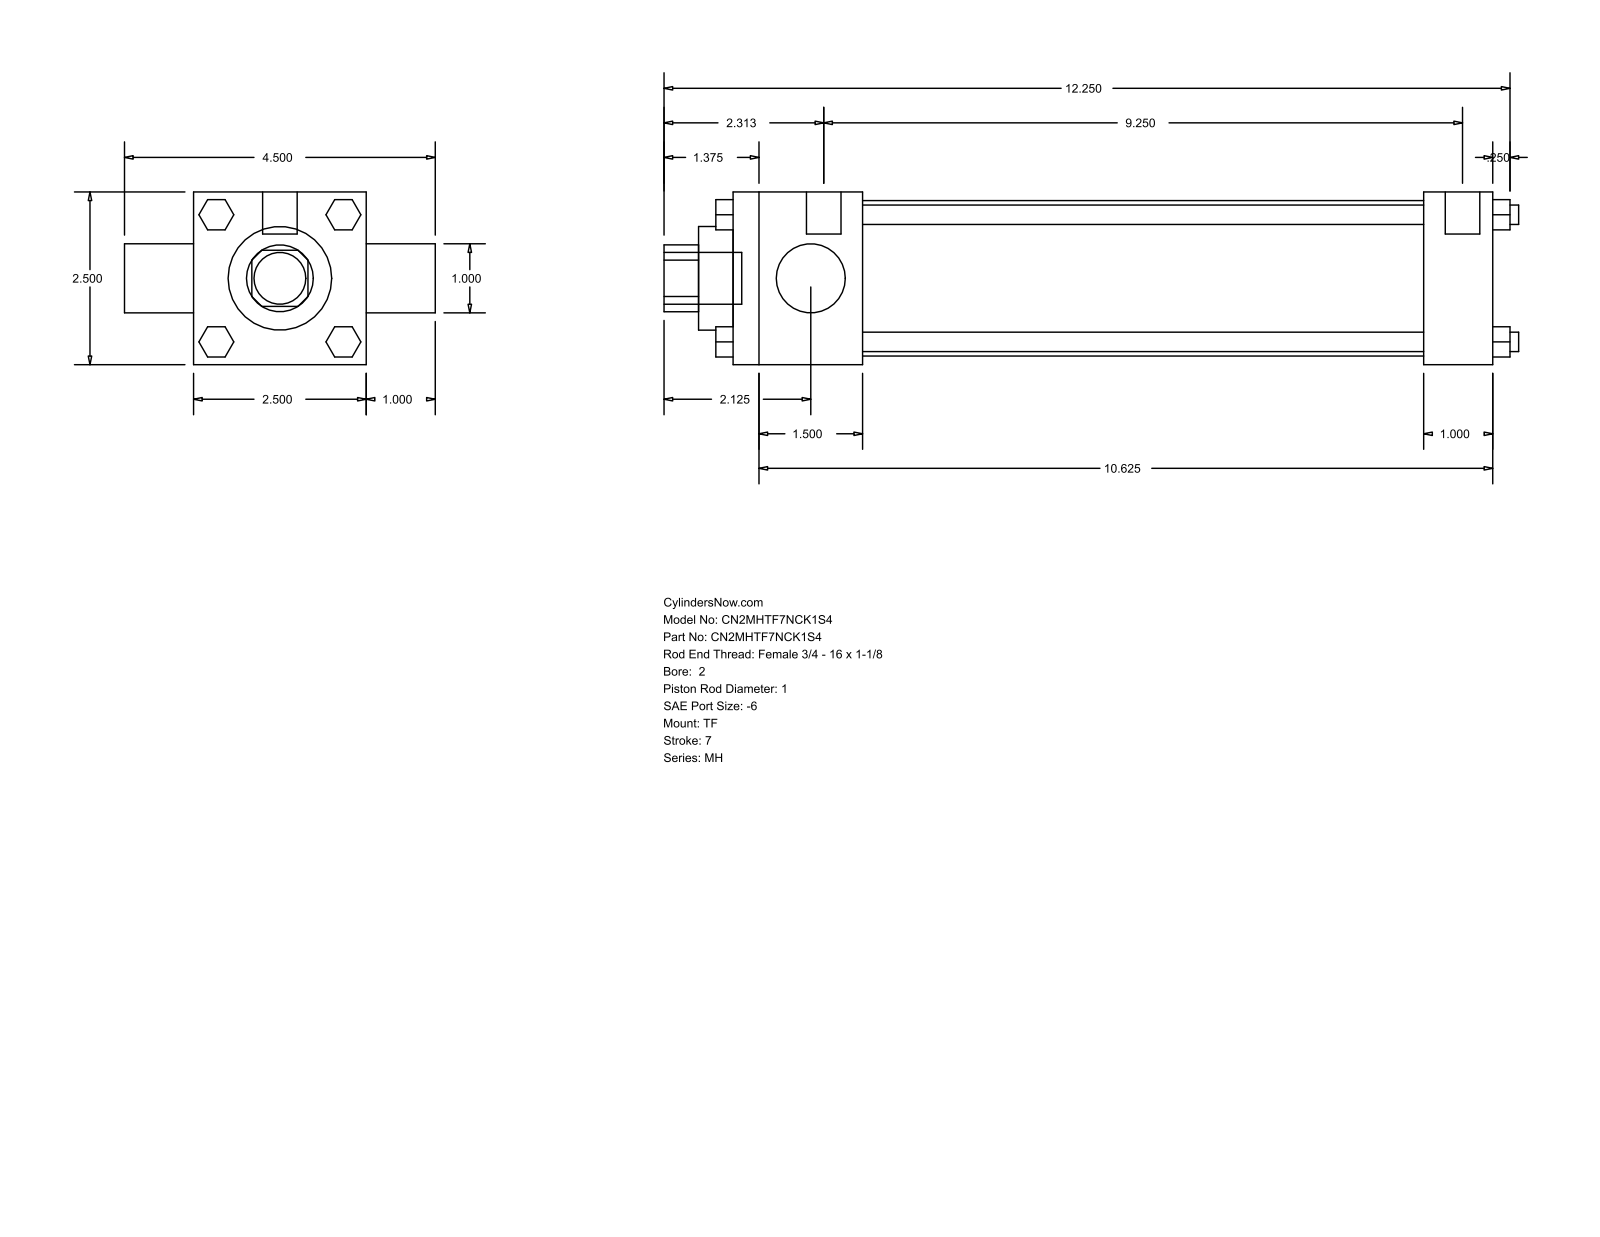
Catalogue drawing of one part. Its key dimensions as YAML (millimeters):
part_name: "MH_TF__0200_1"
step_written_by: "GSSL Pune (CONFIG_CONTROL_DESIGN)"
units: millimeters
bodies: {solids: 0, faces: 120, planar: 92, cylindrical: 28, other: 0}
overall_size: [314.32, 114.3, 63.5]
round_holes:
  - {diameter: 25.4, count: 2}
  - {diameter: 38.1, count: 1}
  - {diameter: 57.15, count: 1}
round_bosses_or_shafts:
  - {diameter: 7.14, count: 4}
  - {diameter: 5.56, count: 3}
  - {diameter: 12.7, count: 2}
  - {diameter: 19.05, count: 1}
partial_cylinders:
  - {radius: 12.29, count: 1}
face_to_face_distances: [63.5, 279.4, 25.4, 47.63, 254, 206.37, 231.77, 88.9, 292.1, 6.35]
